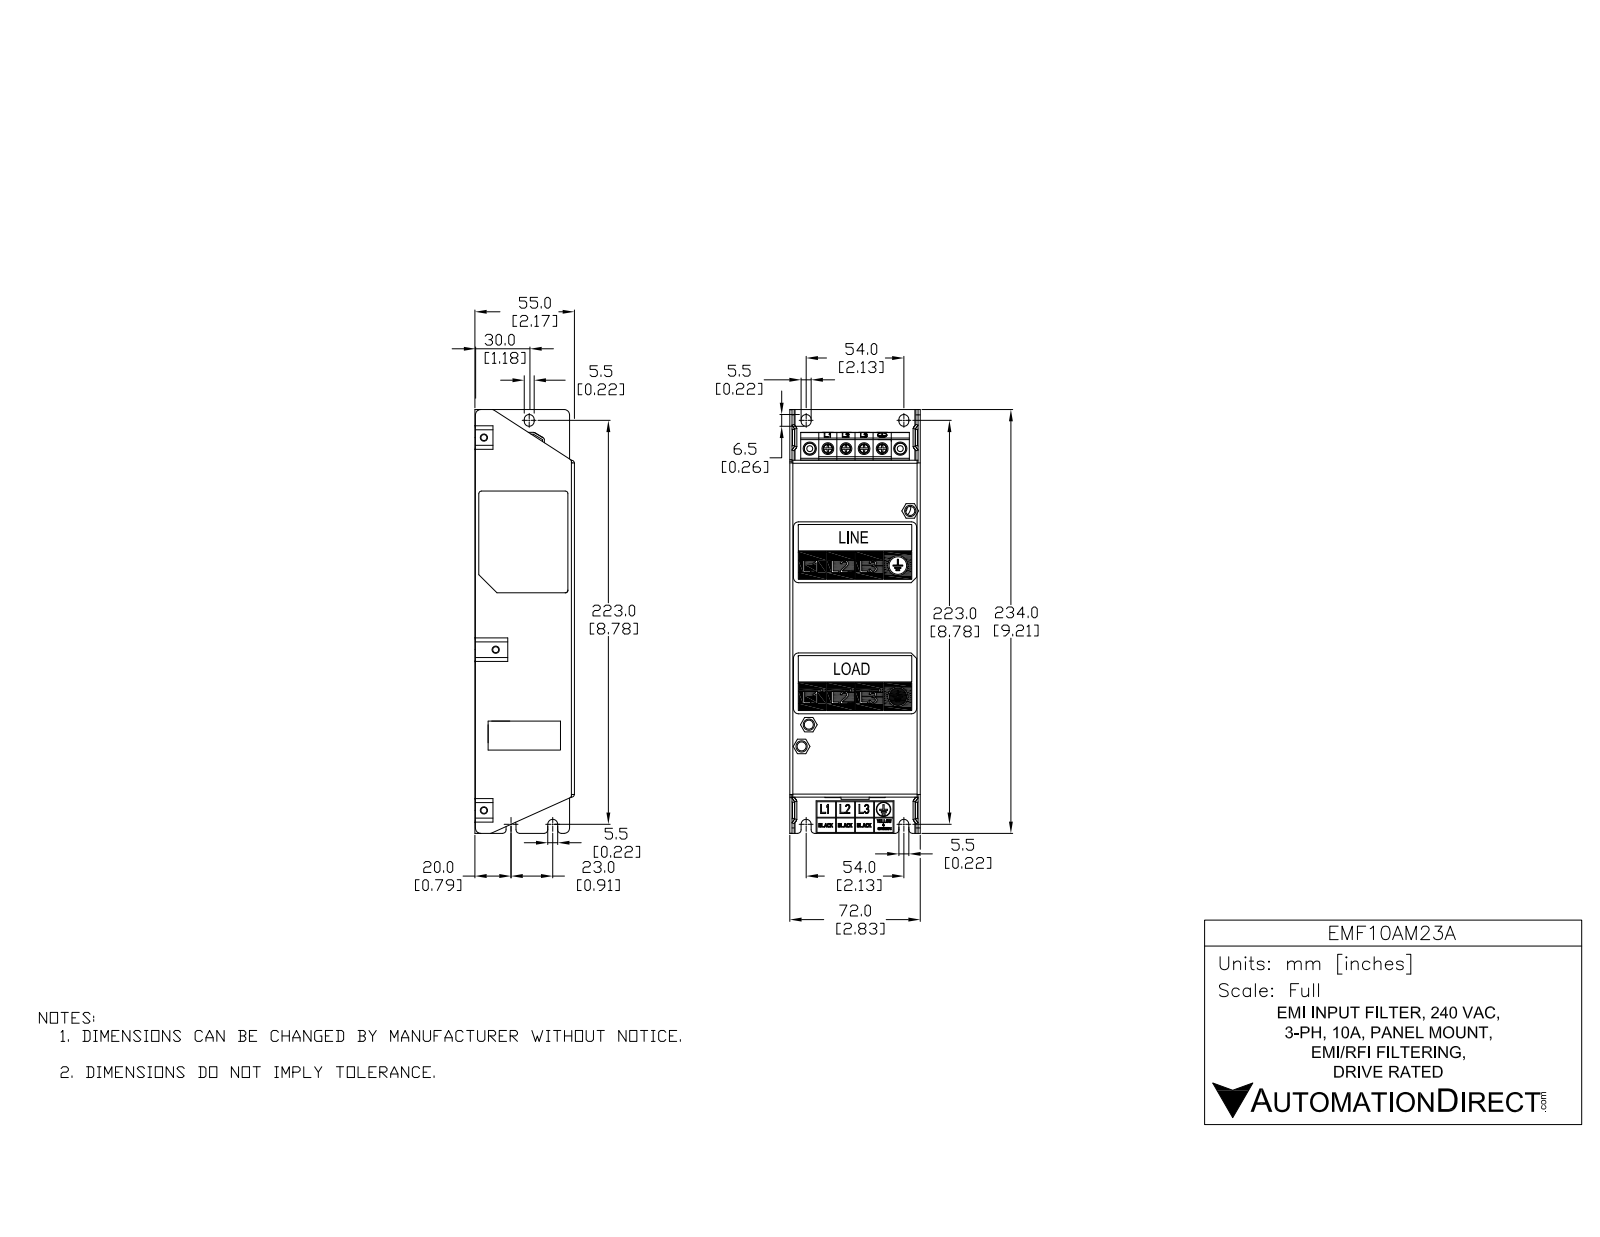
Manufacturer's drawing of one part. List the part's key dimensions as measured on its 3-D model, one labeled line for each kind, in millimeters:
Part name (STEP PRODUCT): EMI A PRT0109 Shell CASE COMPLETE With TB & Label with Sketches wo surf 2 C Coord 1 fXT 2 r1B
STEP written by: SolidWorks 2017 (AUTOMOTIVE_DESIGN)
Units: millimetres
Bodies: 16 solids, 3875 faces (2746 planar, 597 cylindrical, 532 other)
Overall size (bounding box): 234 × 72 × 55.1
Volume: 97 500 mm³ · Surface area: 173 400 mm²
Round holes (diameter × count): ⌀5.5 ×11, ⌀2.1 ×6, ⌀2.4 ×6, ⌀3.6 ×4, ⌀4 ×3, ⌀3 ×2, ⌀5 ×2, ⌀13 ×1
Round bosses / shafts (diameter × count): ⌀5 ×11, ⌀6.3 ×8, ⌀3.9 ×8, ⌀2.3 ×6, ⌀2 ×6, ⌀8 ×4, ⌀5.2 ×2, ⌀4.5 ×1
Partial cylindrical surfaces — rounded edges, fillets, slot ends (radius × count): R1 ×21, R2 ×14, R0.5 ×10, R1.2 ×10, R2.1 ×8, R2.8 ×8, R3.1 ×8, R3.3 ×8
Main face-to-face distances: 1.2, 70.8, 69.6, 0.5, 53.4, 52.2, 53.9, 52.7, 72, 1
Hole centre spacings: 10, 17.2, 14, 20, 24.4, 33.1, 11.3, 12
